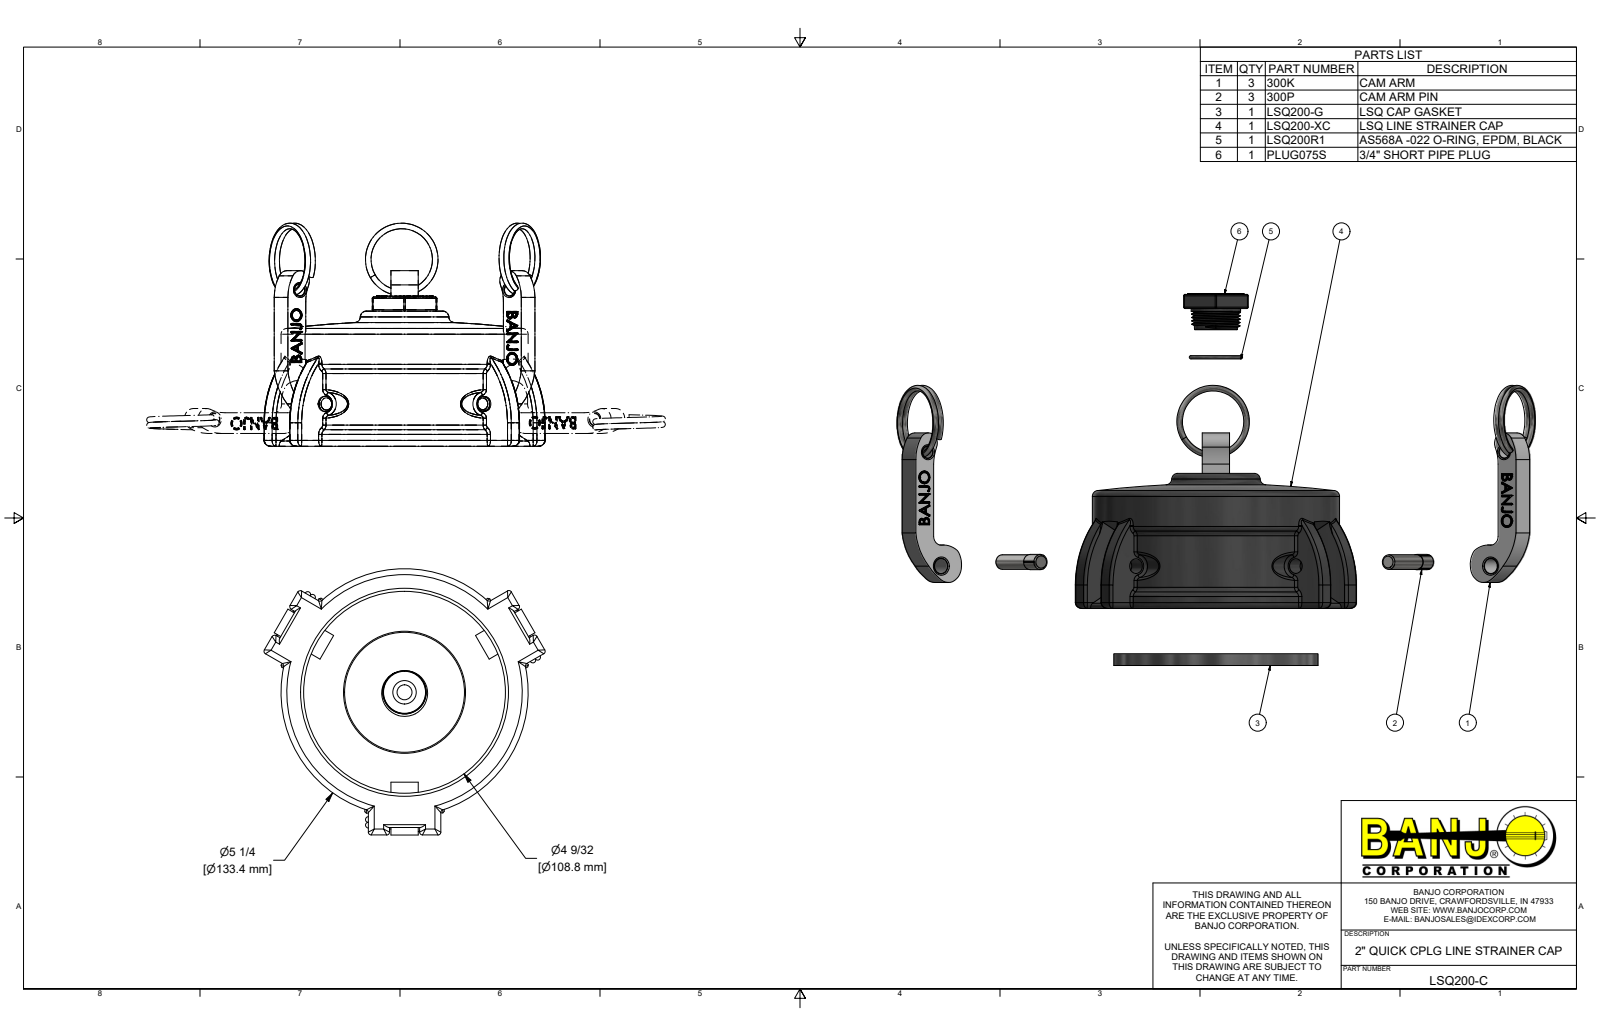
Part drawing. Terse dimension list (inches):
name: LSQ200-C; LSQ200-XC; 300K; 300XK (+5 more)
written by: Autodesk Inventor 2019 (AUTOMOTIVE_DESIGN)
unit: in
bodies: 13 solids, 2518 faces (640 planar, 683 cylindrical, 1195 other)
size: 19.064 × 5.974 × 5.656
volume: 30.64 in³; area: 255.5 in²
holes: 3× ⌀0.25, 3× ⌀0.313, 3× ⌀0.319, 1× ⌀0.5, 1× ⌀2.55, 1× ⌀2.59, 1× ⌀4.165, 1× ⌀4.285, 1× ⌀4.406
bosses: 3× ⌀0.325, 3× ⌀0.311, 1× ⌀5.25, 1× ⌀4.34, 1× ⌀1.05
rounds: 353× R0.006, 51× R0.005, 27× R0.06, 18× R0.03, 15× R0.125, 6× R0.929, 5× R0.25, 3× R0.188
face distances: 0.25, 1.79, 2.04, 2.14, 0.35, 0.1, 0.45, 0.03, 0.61, 1.09
hole spacings: 2.442
